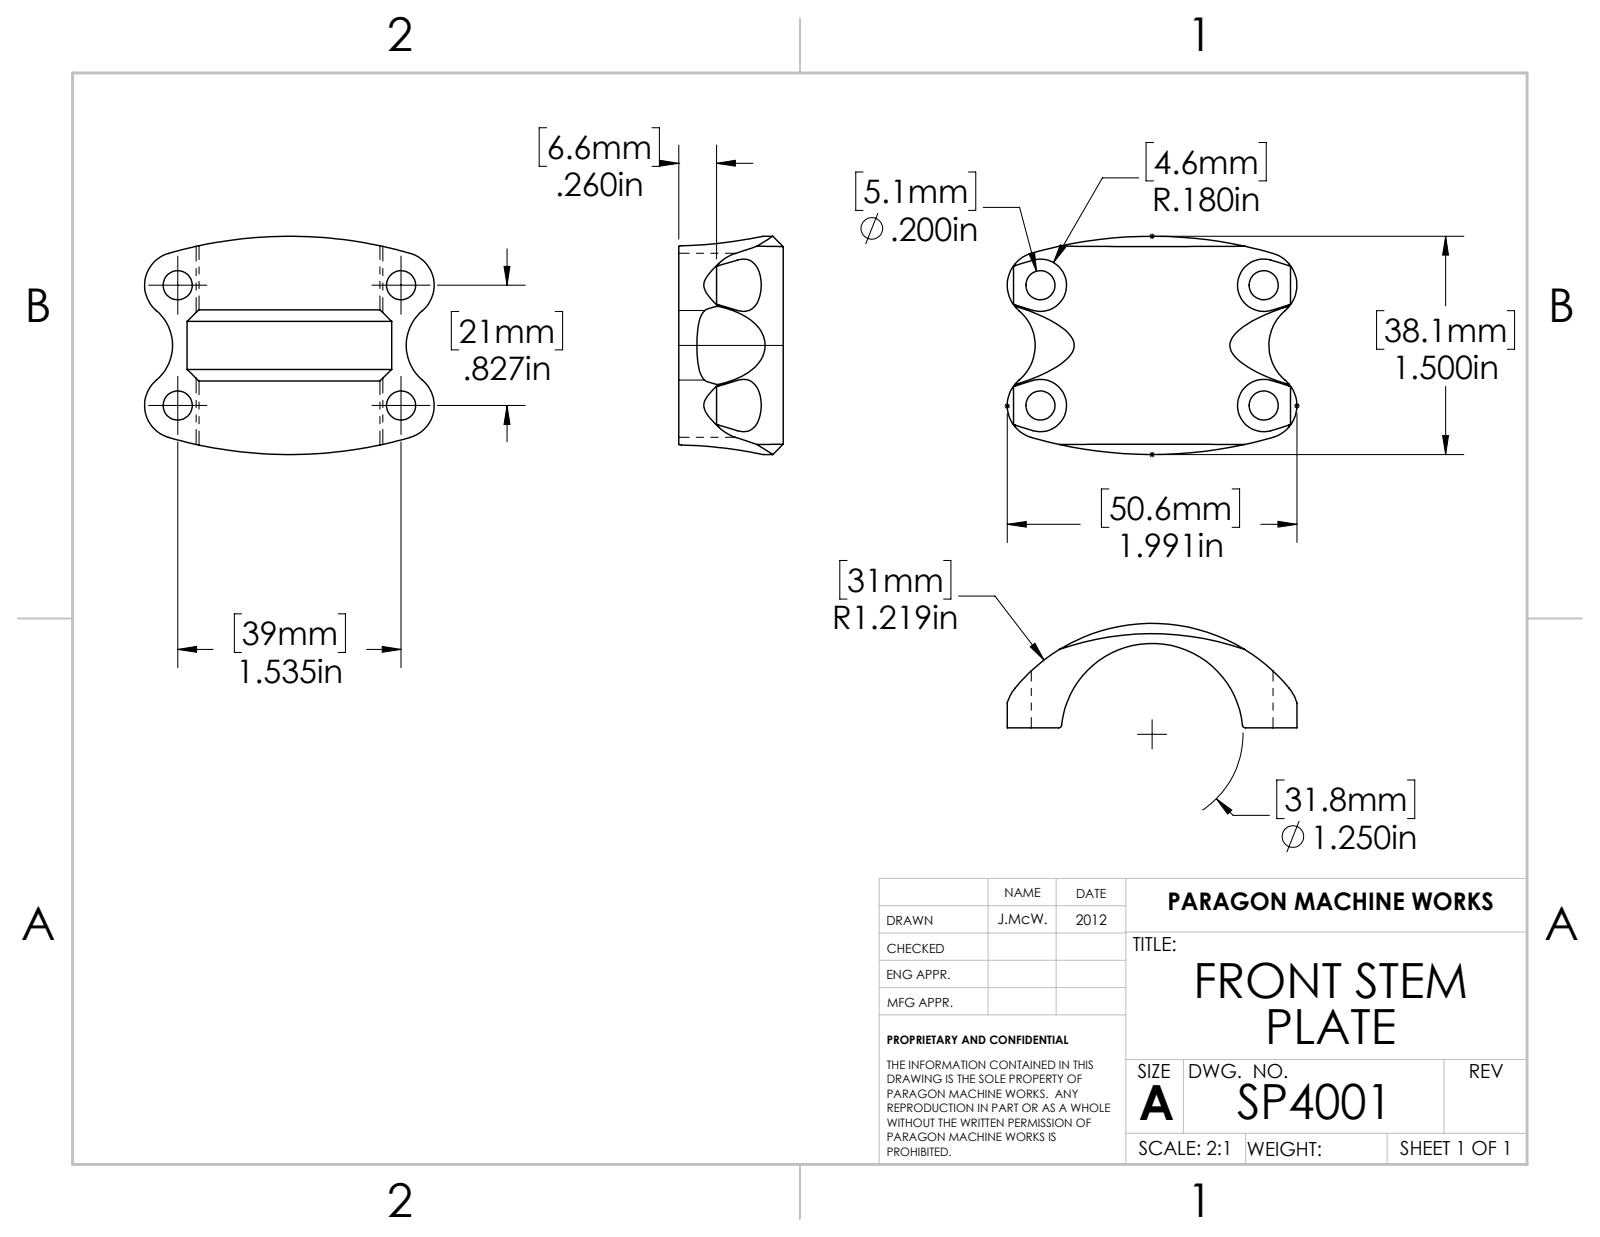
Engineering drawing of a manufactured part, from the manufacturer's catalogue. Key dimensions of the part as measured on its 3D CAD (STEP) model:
Part name (STEP PRODUCT): SP4001
STEP written by: SolidWorks 2012 (AUTOMOTIVE_DESIGN)
Units: millimetres
Bodies: 1 solid, 50 faces (8 planar, 36 cylindrical, 6 other)
Overall size (bounding box): 50.58 × 38.1 × 18.24
Volume: 8 563 mm³ · Surface area: 6 009 mm²
Round holes (diameter × count): ⌀5.08 ×4
Partial cylindrical surfaces — rounded edges, fillets, slot ends (radius × count): R4.57 ×4, R5.79 ×4, R74.78 ×4, R0.51 ×2, R7.62 ×2, R7.94 ×2, R76 ×2, R15.88 ×1
Main face-to-face distances: 6.61, 8.4
Hole centre spacings: 21, 39, 44.29
